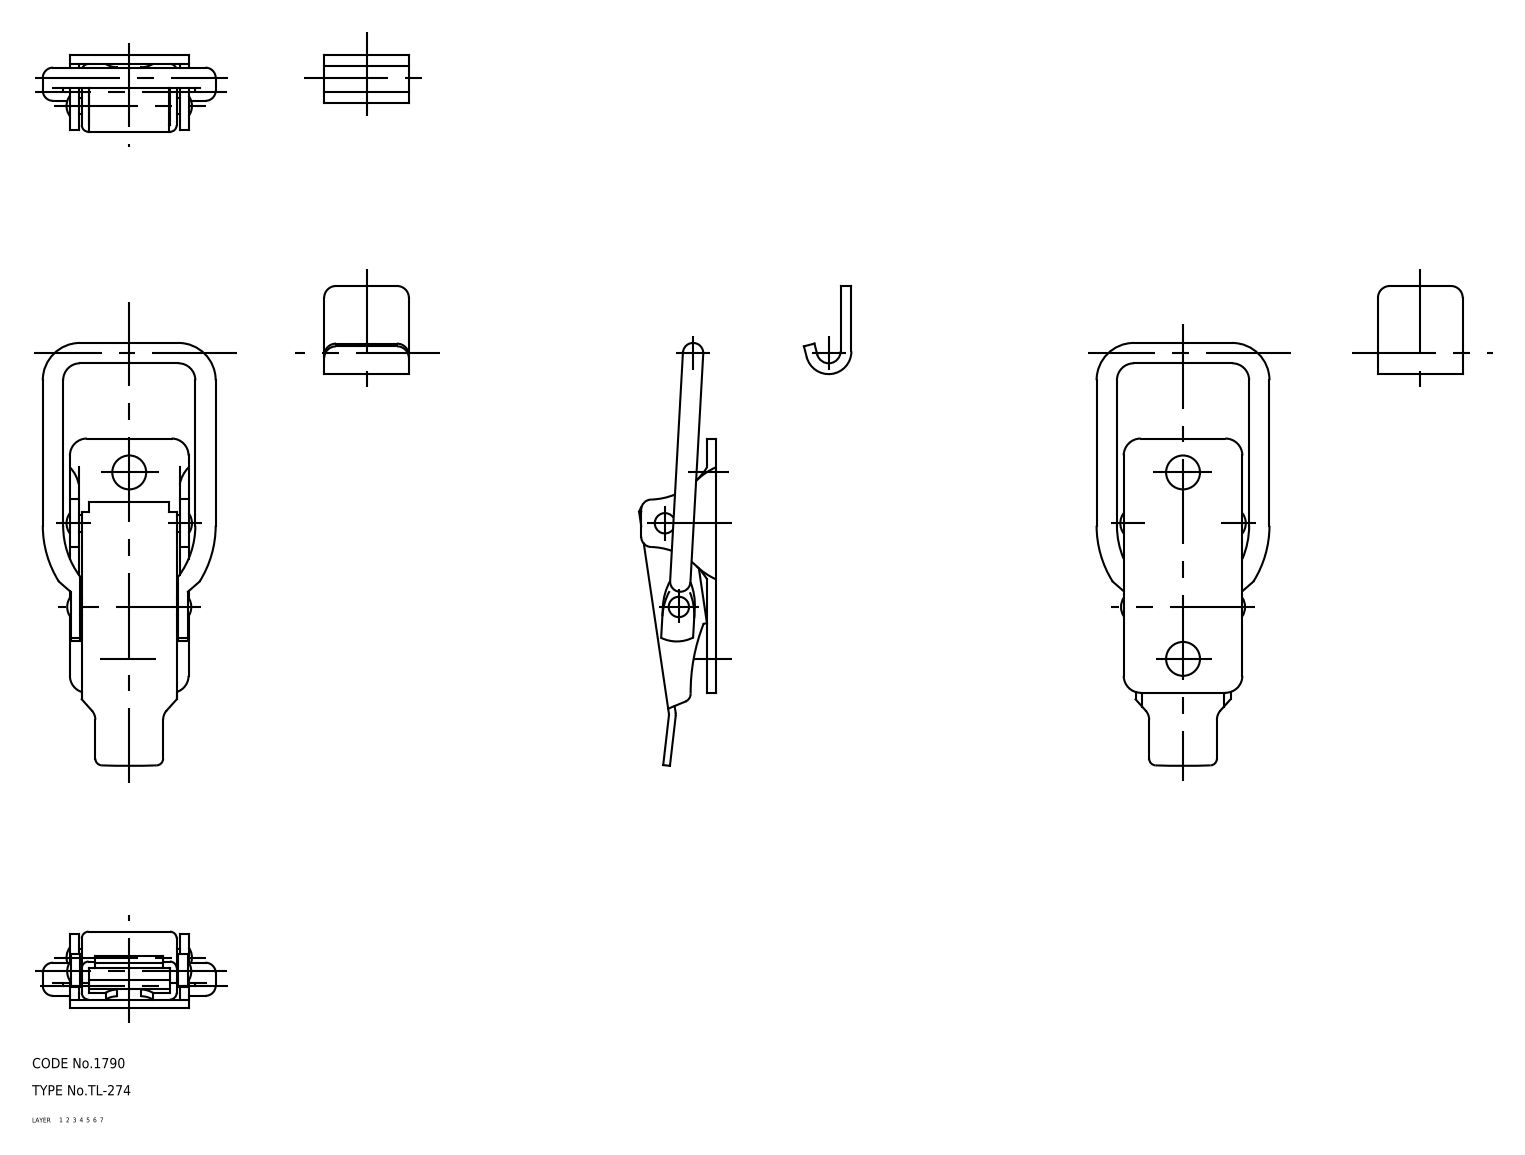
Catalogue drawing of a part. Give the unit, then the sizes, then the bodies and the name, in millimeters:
Units: millimetres
Overall size (bounding box): 141.55 × 51 × 22.59
Volume: 26 728 mm³ · Surface area: 24 349 mm²
Bodies: 8 solids, 207 faces (0 planar, 0 cylindrical, 207 other)
Part name (STEP PRODUCT): arm; plate; shaft_B; shaft_A (+4 more)
STEP written by: CADfix (AUTOMOTIVE_DESIGN)
